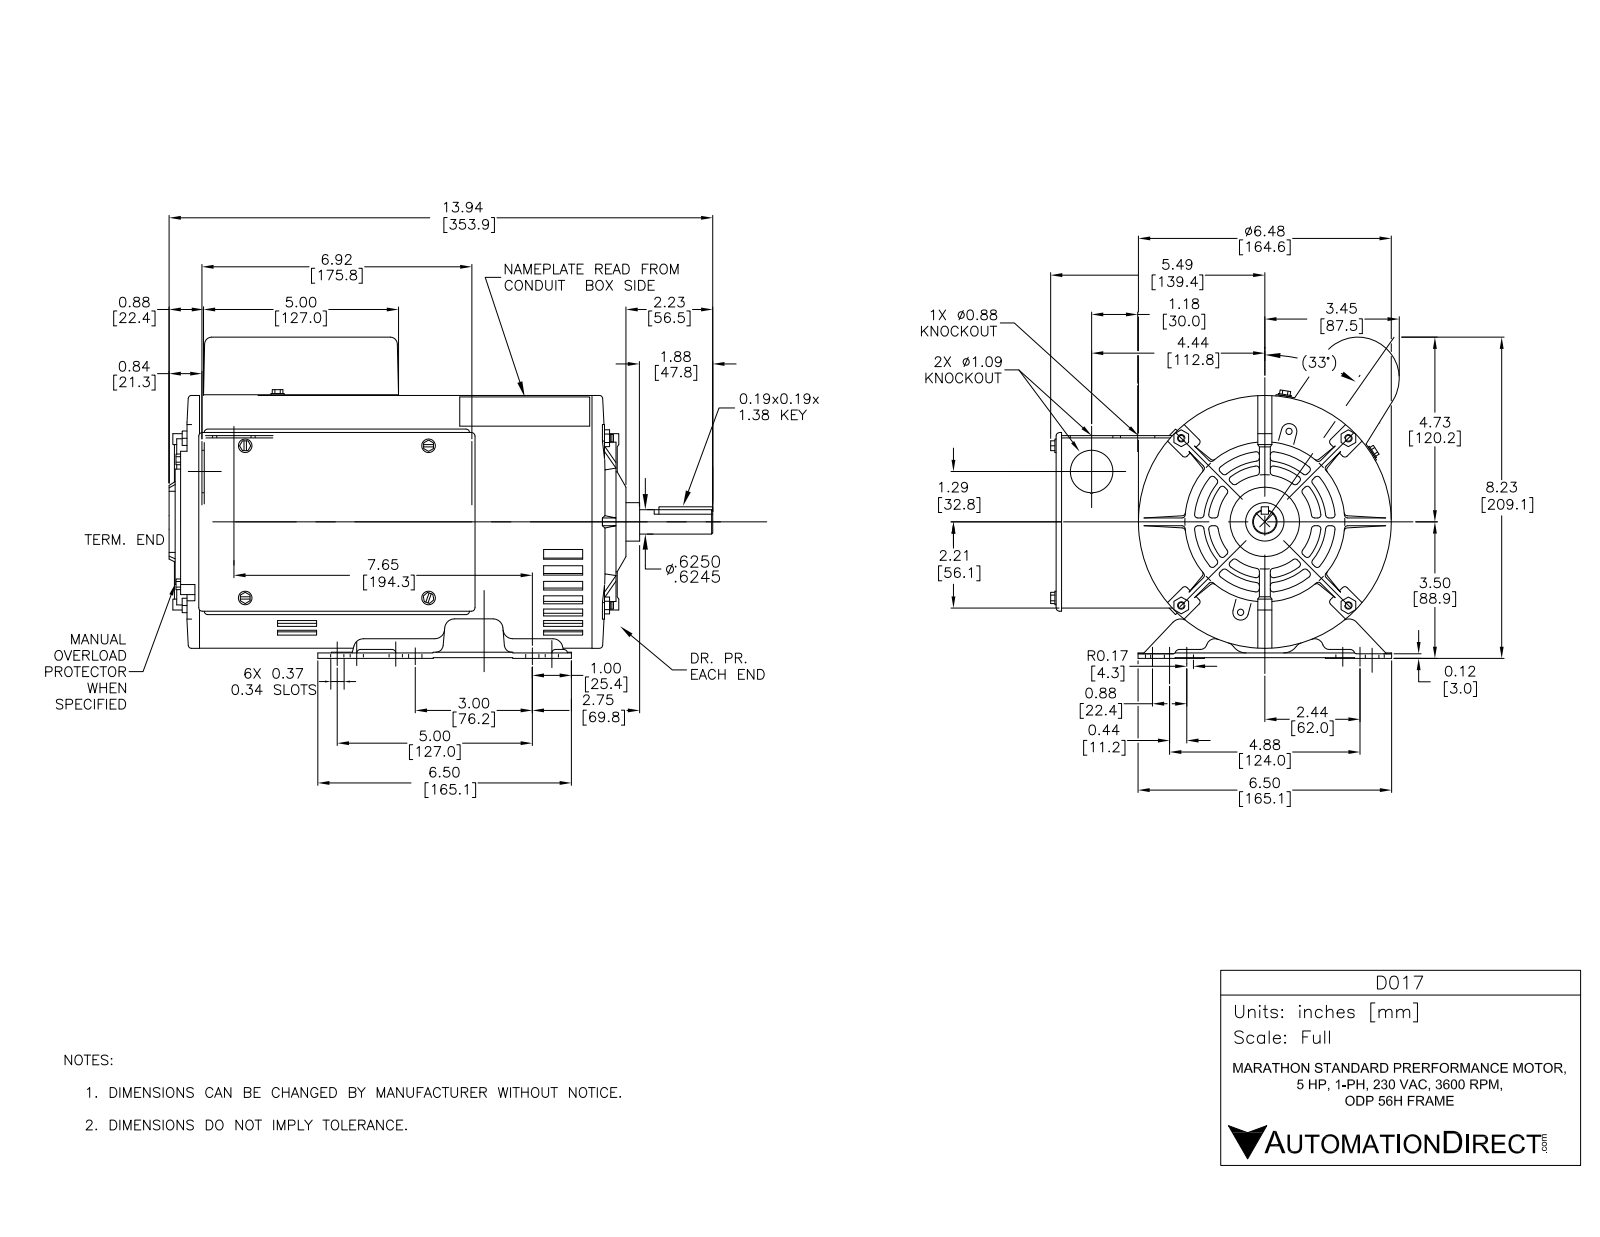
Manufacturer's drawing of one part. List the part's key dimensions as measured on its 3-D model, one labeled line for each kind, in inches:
Part name (STEP PRODUCT): D017 1st b4
STEP written by: SolidWorks 2017 (AUTOMOTIVE_DESIGN)
Units: inches
Bodies: 20 solids, 3772 faces (1402 planar, 805 cylindrical, 1565 other)
Overall size (bounding box): 14.129 × 8.972 × 8.135
Volume: 50.13 in³ · Surface area: 1 060 in²
Round holes (diameter × count): ⌀0.22 ×8, ⌀0.31 ×8, ⌀0.345 ×6, ⌀0.153 ×5, ⌀0.145 ×4, ⌀0.15 ×4, ⌀0.188 ×4, ⌀0.193 ×4, ⌀0.25 ×4, ⌀0.125 ×2, ⌀0.144 ×2, ⌀0.504 ×2
Round bosses / shafts (diameter × count): ⌀0.164 ×7, ⌀0.399 ×4, ⌀0.335 ×4, ⌀0.19 ×4, ⌀0.166 ×4, ⌀0.335 ×3, ⌀0.34 ×2, ⌀6.436 ×1
Partial cylindrical surfaces — rounded edges, fillets, slot ends (radius × count): R0.06 ×55, R0.25 ×44, R0.05 ×34, R0.08 ×30, R0.03 ×29, R0.09 ×23, R0.02 ×21, R0.1 ×16
Main face-to-face distances: 0.06, 4.36, 0.044, 6.93, 4.3, 4.42, 0.119, 0.026, 1.263, 1.323
Hole centre spacings: 4.283, 0.035, 3.027, 3.03, 3.9, 4.28, 4.285, 4.7
